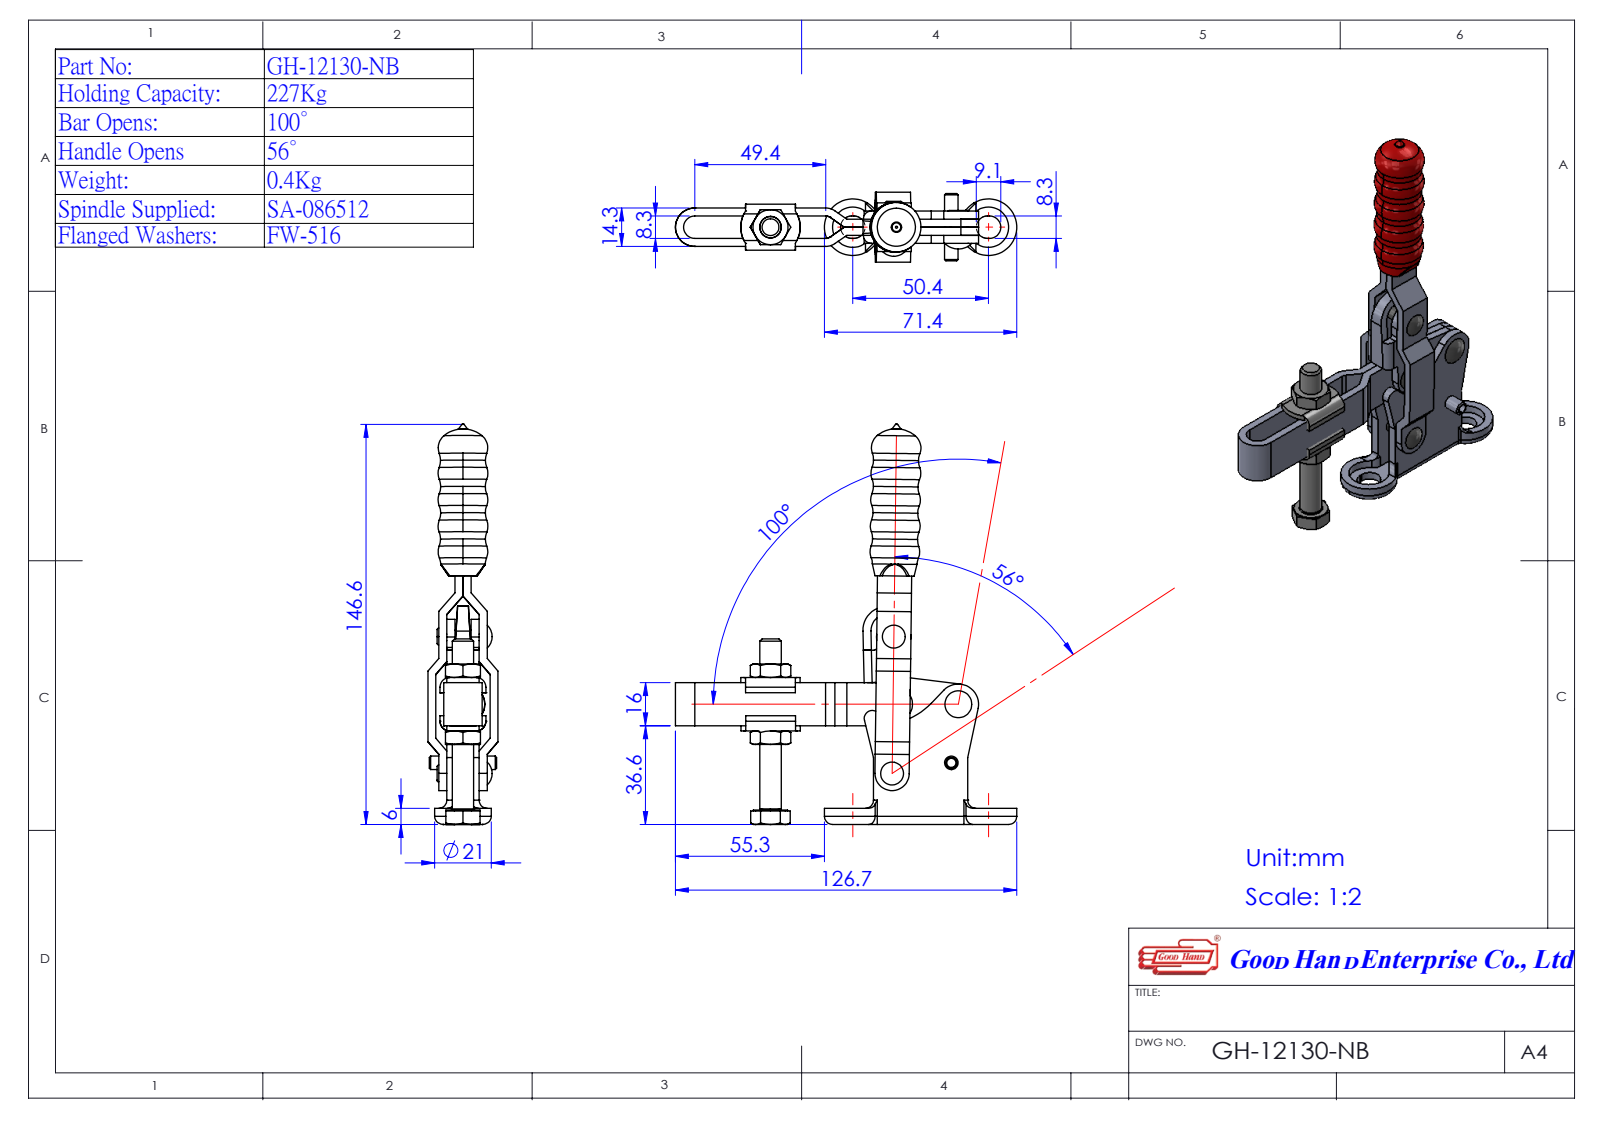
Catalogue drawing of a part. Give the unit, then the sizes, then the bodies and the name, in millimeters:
Units: millimetres
Overall size (bounding box): 145.96 × 126.69 × 26.7
Round holes (diameter × count): ⌀4 ×4, ⌀3.4 ×1
Round bosses / shafts (diameter × count): ⌀6.4 ×2, ⌀17.61 ×1, ⌀10 ×1, ⌀8 ×1, ⌀6.3 ×1, ⌀5 ×1
Partial cylindrical surfaces — rounded edges, fillets, slot ends (radius × count): R3 ×7, R7.5 ×6, R4.15 ×5, R1 ×4, R1.5 ×4, R1 ×2, R4 ×2, R4 ×2
Main face-to-face distances: 3, 6, 9, 1.15, 4.15, 7.15, 10.15, 12, 13.15, 1.85
Hole centre spacings: 21.9, 22.35, 23.4, 25.13, 25.73, 30.09, 35.14, 35.58
Volume: 54 668 mm³ · Surface area: 35 422 mm²
Bodies: 5 solids, 382 faces (165 planar, 122 cylindrical, 95 other)
Part name (STEP PRODUCT): Group6^GH-12130-NB(簡化)-1; Group5^GH-12130-NB(簡化)-1; Group2^GH-12130-NB(簡化)-1; Group1^GH-12130-NB(簡化)-1 (+2 more)
STEP written by: SolidWorks 2016 (AUTOMOTIVE_DESIGN)
